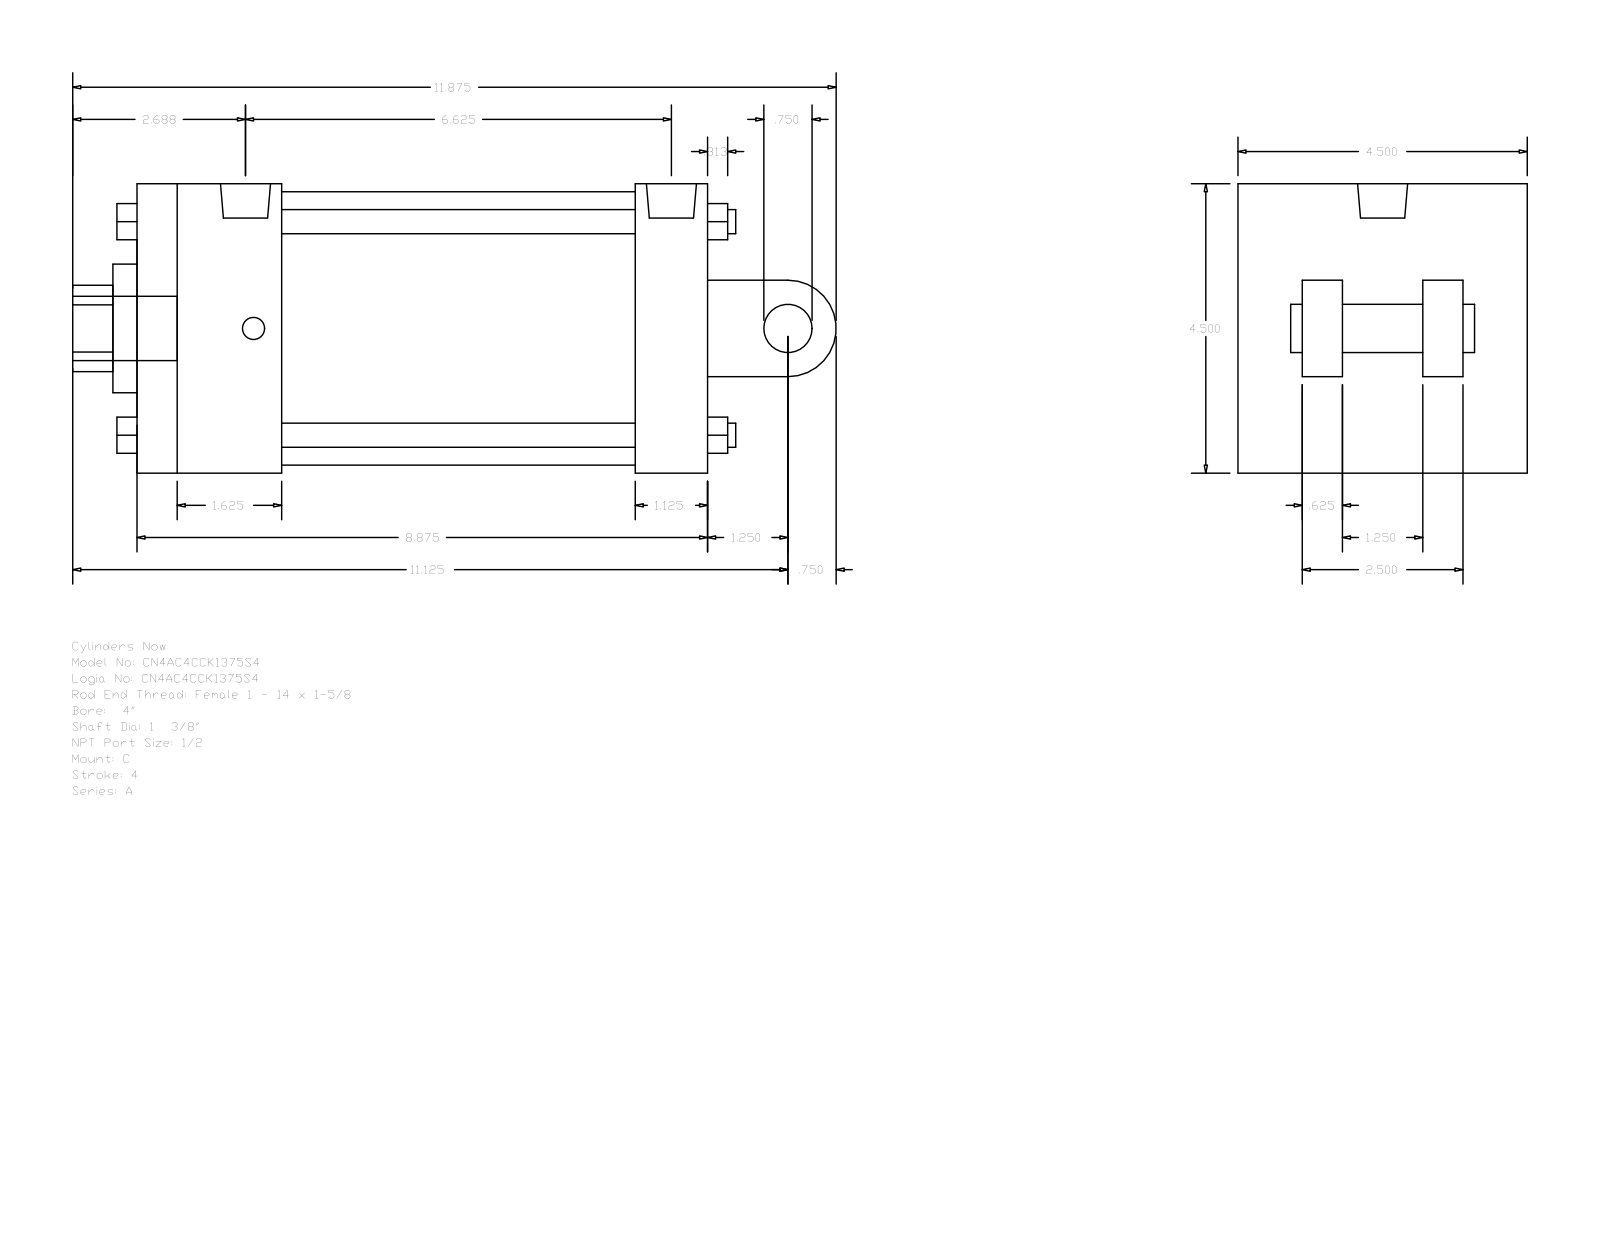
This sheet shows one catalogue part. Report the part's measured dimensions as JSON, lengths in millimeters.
{"part_name": "A_C__0400_1.375", "step_written_by": "GSSL Pune (CONFIG_CONTROL_DESIGN)", "units": "millimeters", "bodies": {"solids": 0, "faces": 135, "planar": 102, "cylindrical": 33, "other": 0}, "overall_size": [301.62, 114.3, 114.3], "round_holes": [[8.73, 2], [19.77, 1], [34.92, 1], [50.8, 1], [107.95, 1]], "round_bosses_or_shafts": [[9.53, 4], [8.73, 2], [25.4, 1], [19.77, 1], [19.05, 1]], "partial_cylinders_radius": [[17.06, 1], [19.05, 1]], "face_to_face_distances": [114.3, 225.42, 73.03, 28.57, 196.85, 57.15, 139.7, 168.27, 15.87, 41.27], "hole_center_spacings": [3.18]}
